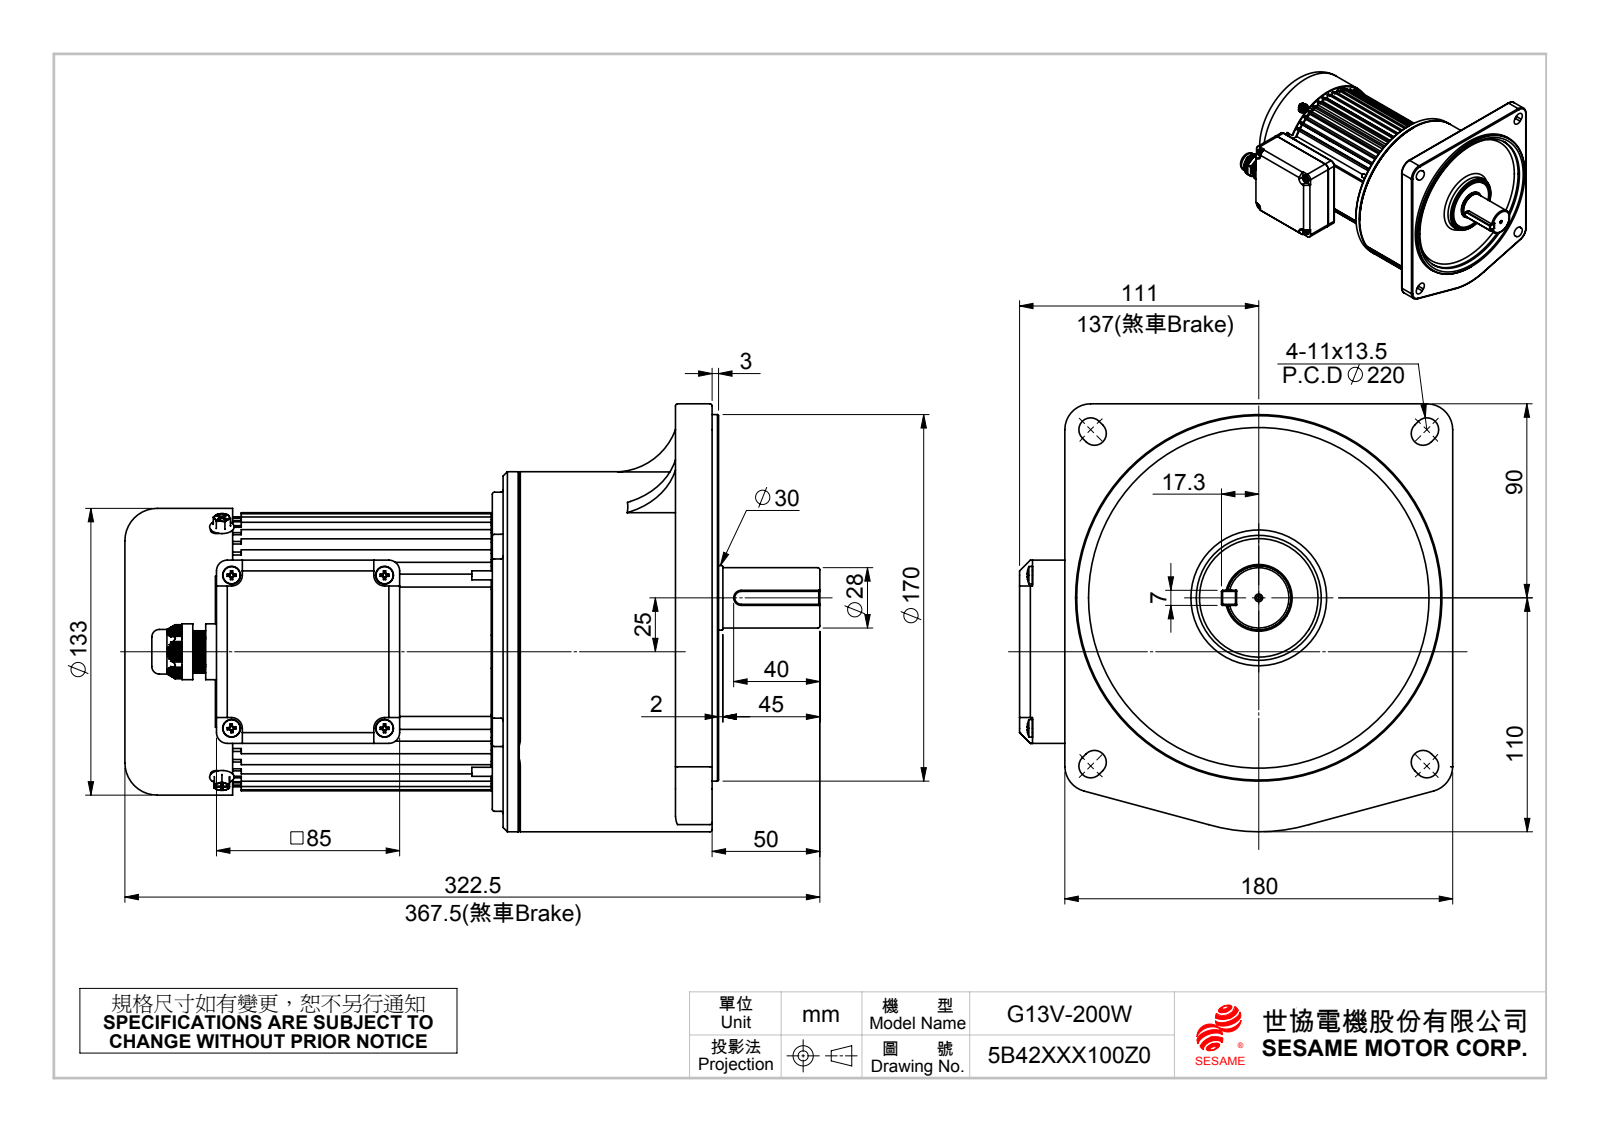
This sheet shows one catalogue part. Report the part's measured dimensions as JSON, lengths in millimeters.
{"part_name": "(標準品)G13V200W(5B42XXX100)(減速比共用); 出線盒下蓋; 成品-塑膠T盒; 7x7xL_40L (+8 more)", "step_written_by": "SolidWorks 2010 (CONFIG_CONTROL_DESIGN)", "units": "millimeters", "bodies": {"solids": 19, "faces": 2799, "planar": 842, "cylindrical": 908, "other": 1049}, "overall_size": [322.5, 201, 198.5], "volume_mm3": 4390000, "surface_area_mm2": 519878, "round_holes": [[5, 11], [3.3, 9], [8, 9], [5.1, 5], [4.2, 3], [2, 1], [7.5, 1], [10.8, 1], [16.5, 1], [30, 1], [31, 1], [53, 1]], "round_bosses_or_shafts": [[8.3, 4], [4.2, 4], [4, 4], [5, 3], [170, 1], [167, 1], [158, 1], [148, 1]], "partial_cylinders_radius": [[1, 84], [3, 16], [1.03, 8], [5, 8], [5.5, 8], [2.75, 6], [8, 5], [2, 4]], "face_to_face_distances": [2, 5, 84.5, 10, 120.5, 12.5, 18, 133, 138, 13], "hole_center_spacings": [89.35, 144.57, 45, 71, 76.01, 11, 11.5, 14.6]}
